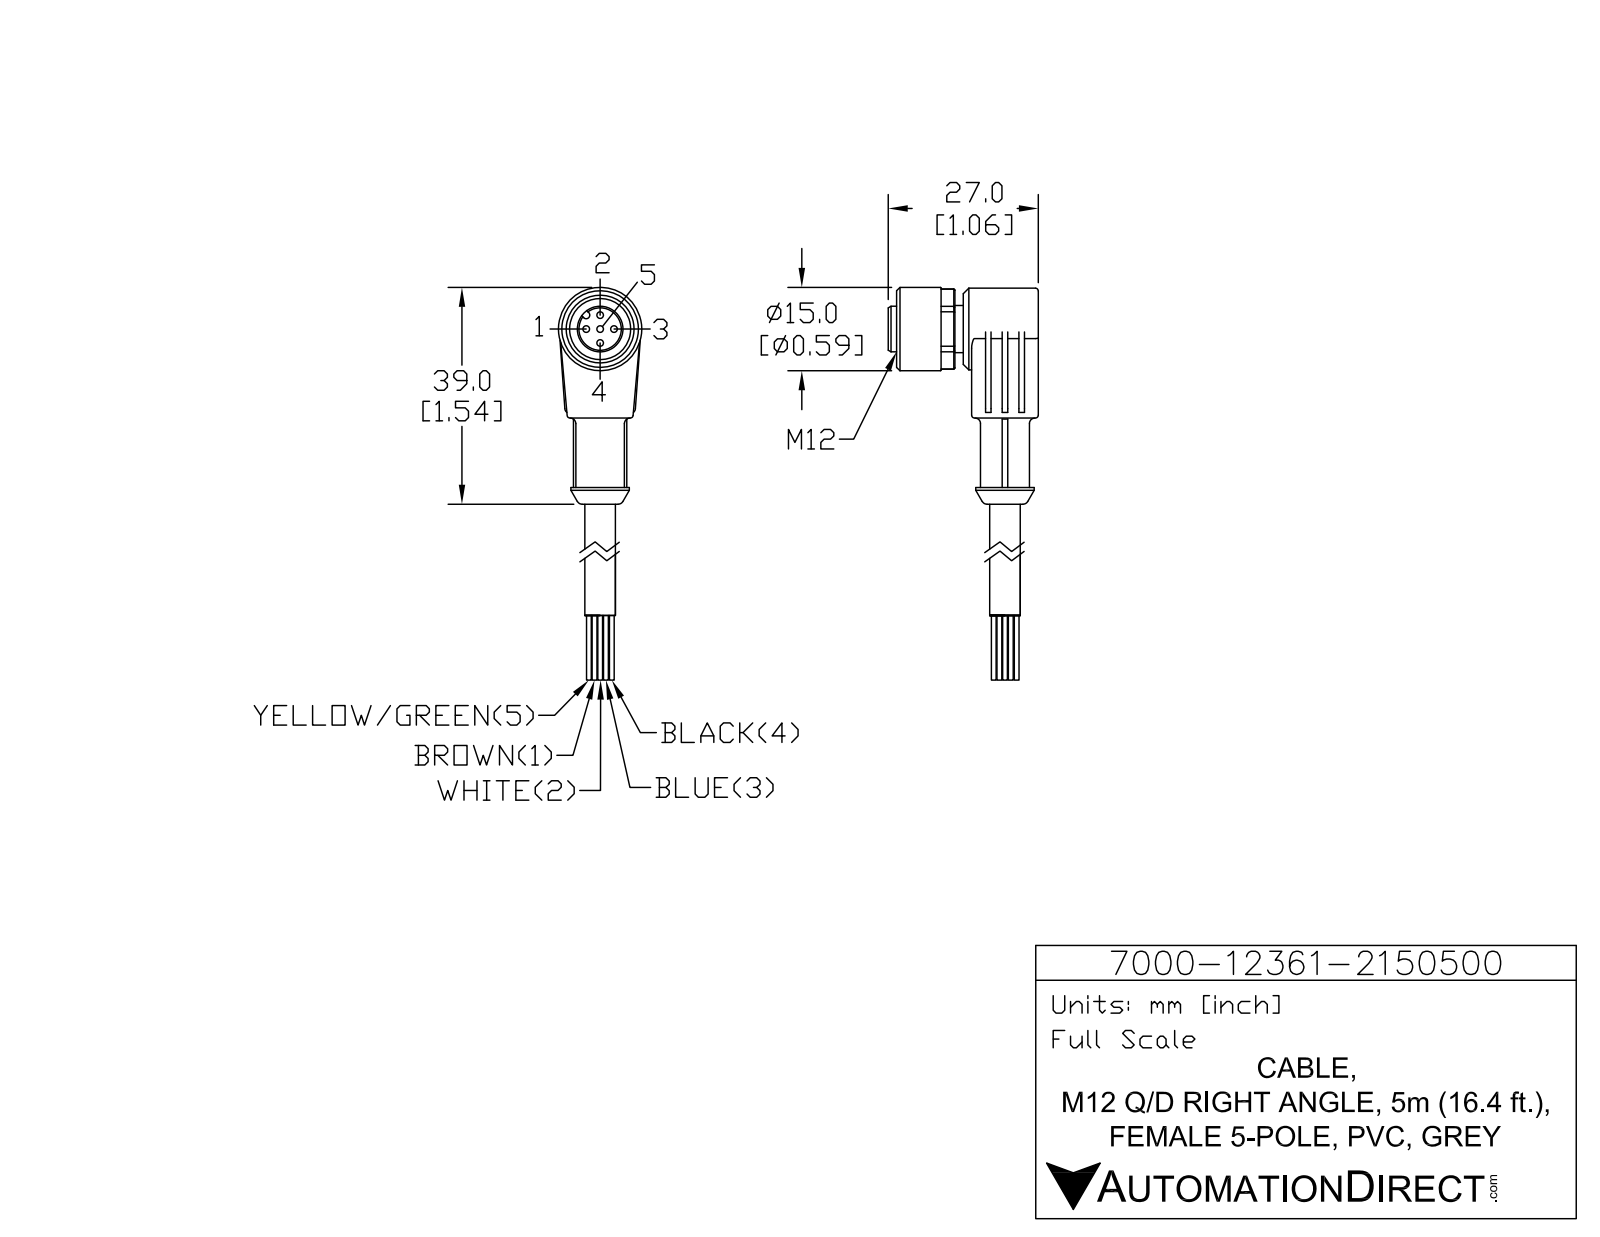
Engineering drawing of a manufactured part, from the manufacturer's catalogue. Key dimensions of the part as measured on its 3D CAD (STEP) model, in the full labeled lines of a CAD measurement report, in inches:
Part name (STEP PRODUCT): 7000-12361-2150500
STEP written by: SolidWorks 2015 (AUTOMOTIVE_DESIGN)
Units: inches
Bodies: 1 solid, 150 faces (61 planar, 60 cylindrical, 29 other)
Overall size (bounding box): 2.323 × 1.063 × 0.591
Volume: 0.415 in³ · Surface area: 5.6 in²
Round holes (diameter × count): ⌀0.047 ×5, ⌀0.189 ×1, ⌀0.433 ×1
Round bosses / shafts (diameter × count): ⌀0.591 ×1, ⌀0.579 ×1, ⌀0.413 ×1, ⌀0.346 ×1, ⌀0.335 ×1, ⌀0.323 ×1, ⌀0.217 ×1
Partial cylindrical surfaces — rounded edges, fillets, slot ends (radius × count): R0.02 ×8, R0.039 ×2, R0.026 ×1, R0.283 ×1
Main face-to-face distances: 0.472, 0.059, 0.118, 0.531, 0.591, 0.217, 0.374, 0.236, 0.315, 0.492
Hole centre spacings: 0.098, 0.139, 0.197
